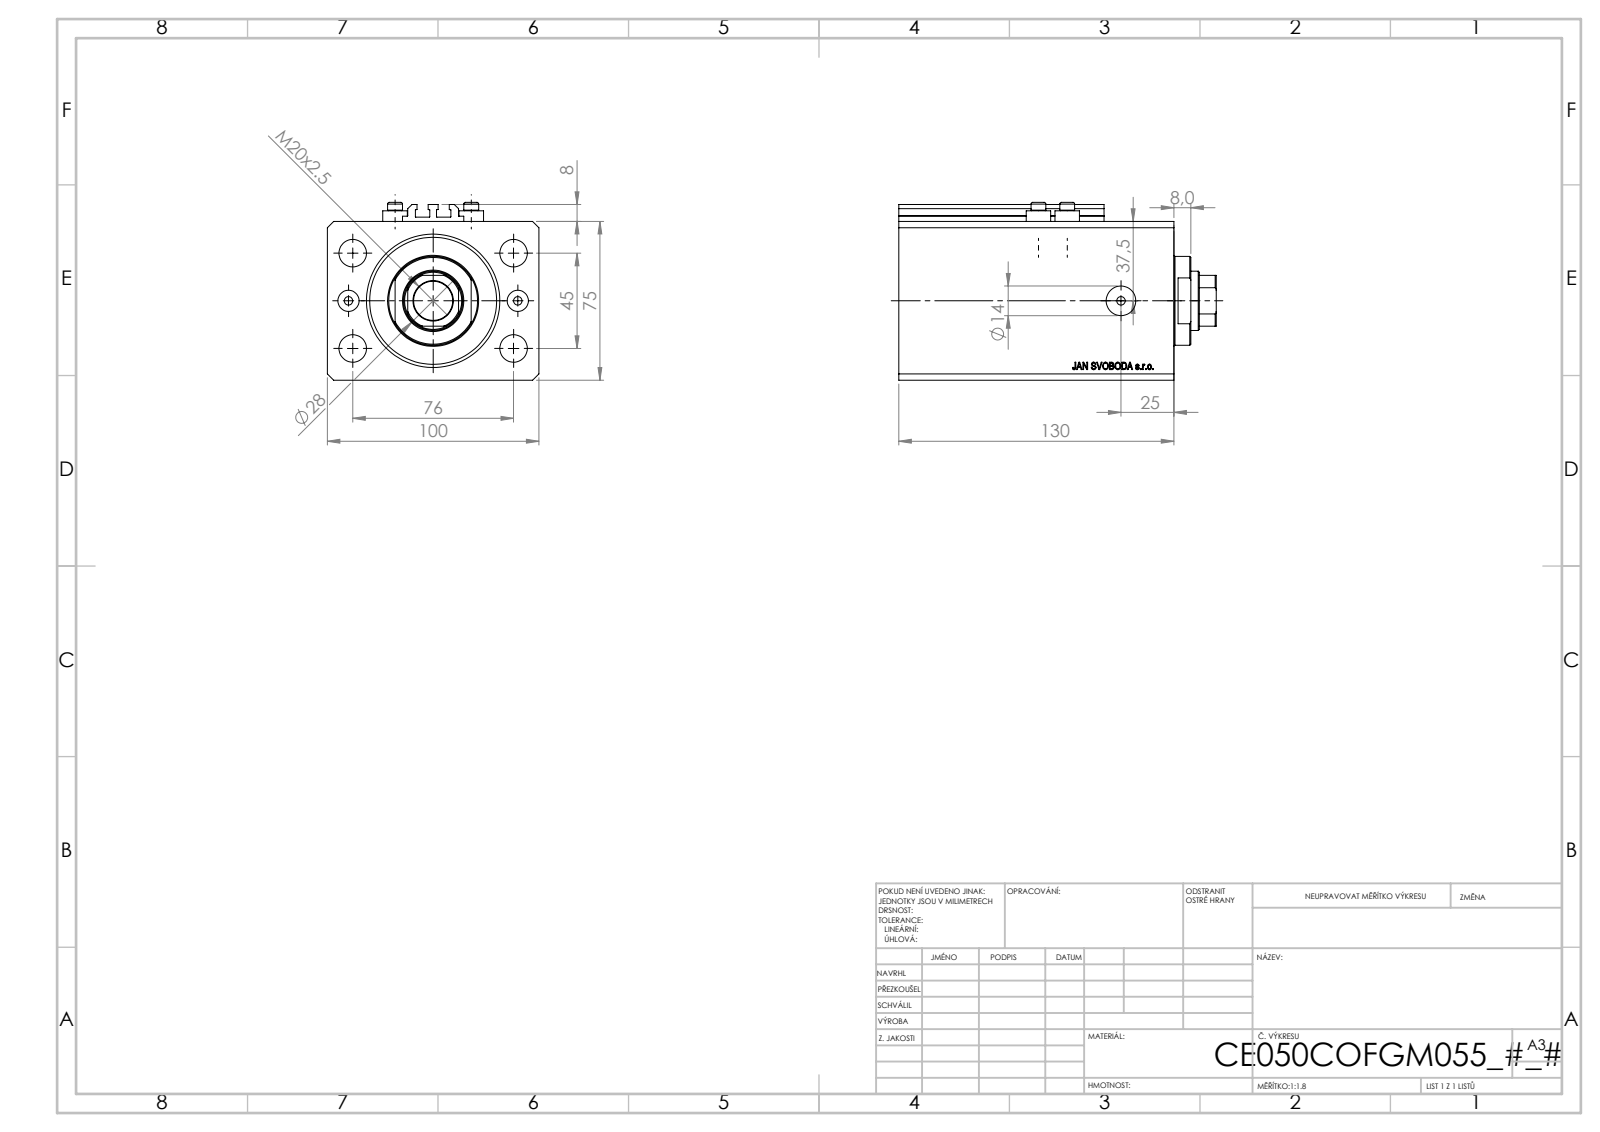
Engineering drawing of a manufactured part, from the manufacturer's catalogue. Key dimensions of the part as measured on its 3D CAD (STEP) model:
Part name (STEP PRODUCT): V250CE_VC_C; ALLEN BOLT V250CE; V250CE_C_Body; V250CE_C_VCP
STEP written by: SolidWorks 2019 (CONFIG_CONTROL_DESIGN)
Units: millimetres
Bodies: 8 solids, 1034 faces (504 planar, 86 cylindrical, 444 other)
Overall size (bounding box): 150 × 100 × 84
Volume: 848 657 mm³ · Surface area: 146 804 mm²
Round holes (diameter × count): ⌀4 ×8, ⌀13 ×4, ⌀10 ×2, ⌀14 ×2, ⌀18.5 ×1, ⌀28 ×1, ⌀50 ×1, ⌀63 ×1
Round bosses / shafts (diameter × count): ⌀11.6 ×4, ⌀7 ×4, ⌀42 ×1
Partial cylindrical surfaces — rounded edges, fillets, slot ends (radius × count): R0.2 ×10, R13.5 ×1
Main face-to-face distances: 75, 100, 130, 11.9, 118.1, 20, 110, 98.1, 55, 8
Hole centre spacings: 22.59, 44.16, 81.18, 13.6, 36, 38.48, 40, 45
